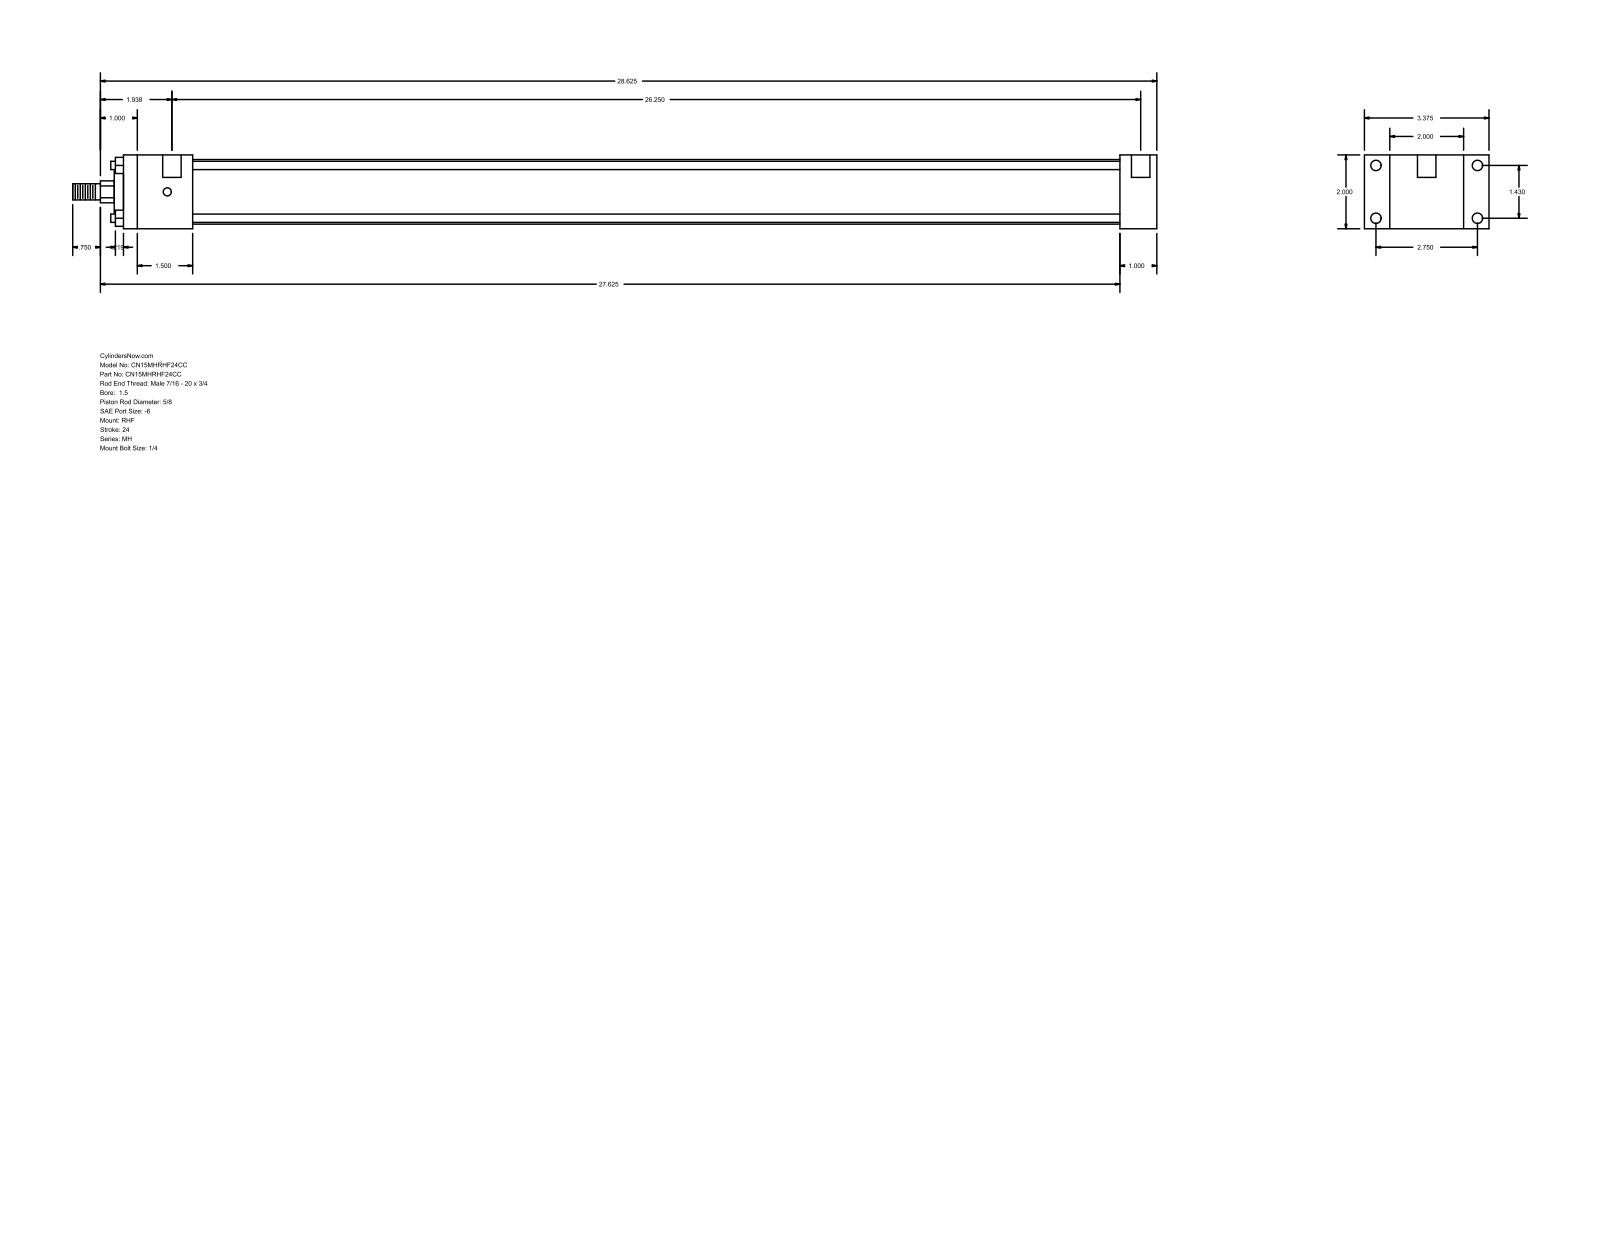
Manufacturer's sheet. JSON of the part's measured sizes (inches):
{"part_name": "MH_RHF__0150_0.625", "step_written_by": "GSSL Pune (CONFIG_CONTROL_DESIGN)", "units": "inches", "bodies": {"solids": 0, "faces": 88, "planar": 60, "cylindrical": 28, "other": 0}, "overall_size": [29.375, 3.375, 2], "round_holes": [[0.219, 4], [0.281, 4], [0.5, 2]], "round_bosses_or_shafts": [[0.225, 4], [1.75, 1], [1.125, 1], [0.625, 1], [0.437, 1]], "partial_cylinders_radius": [[0.297, 1]], "face_to_face_distances": [2, 0.687, 2.687, 1, 27, 28, 3.375, 1.875, 25.125, 26.125], "hole_center_spacings": [1.43, 2.75, 3.099, 26.375, 0.125, 26.25]}
